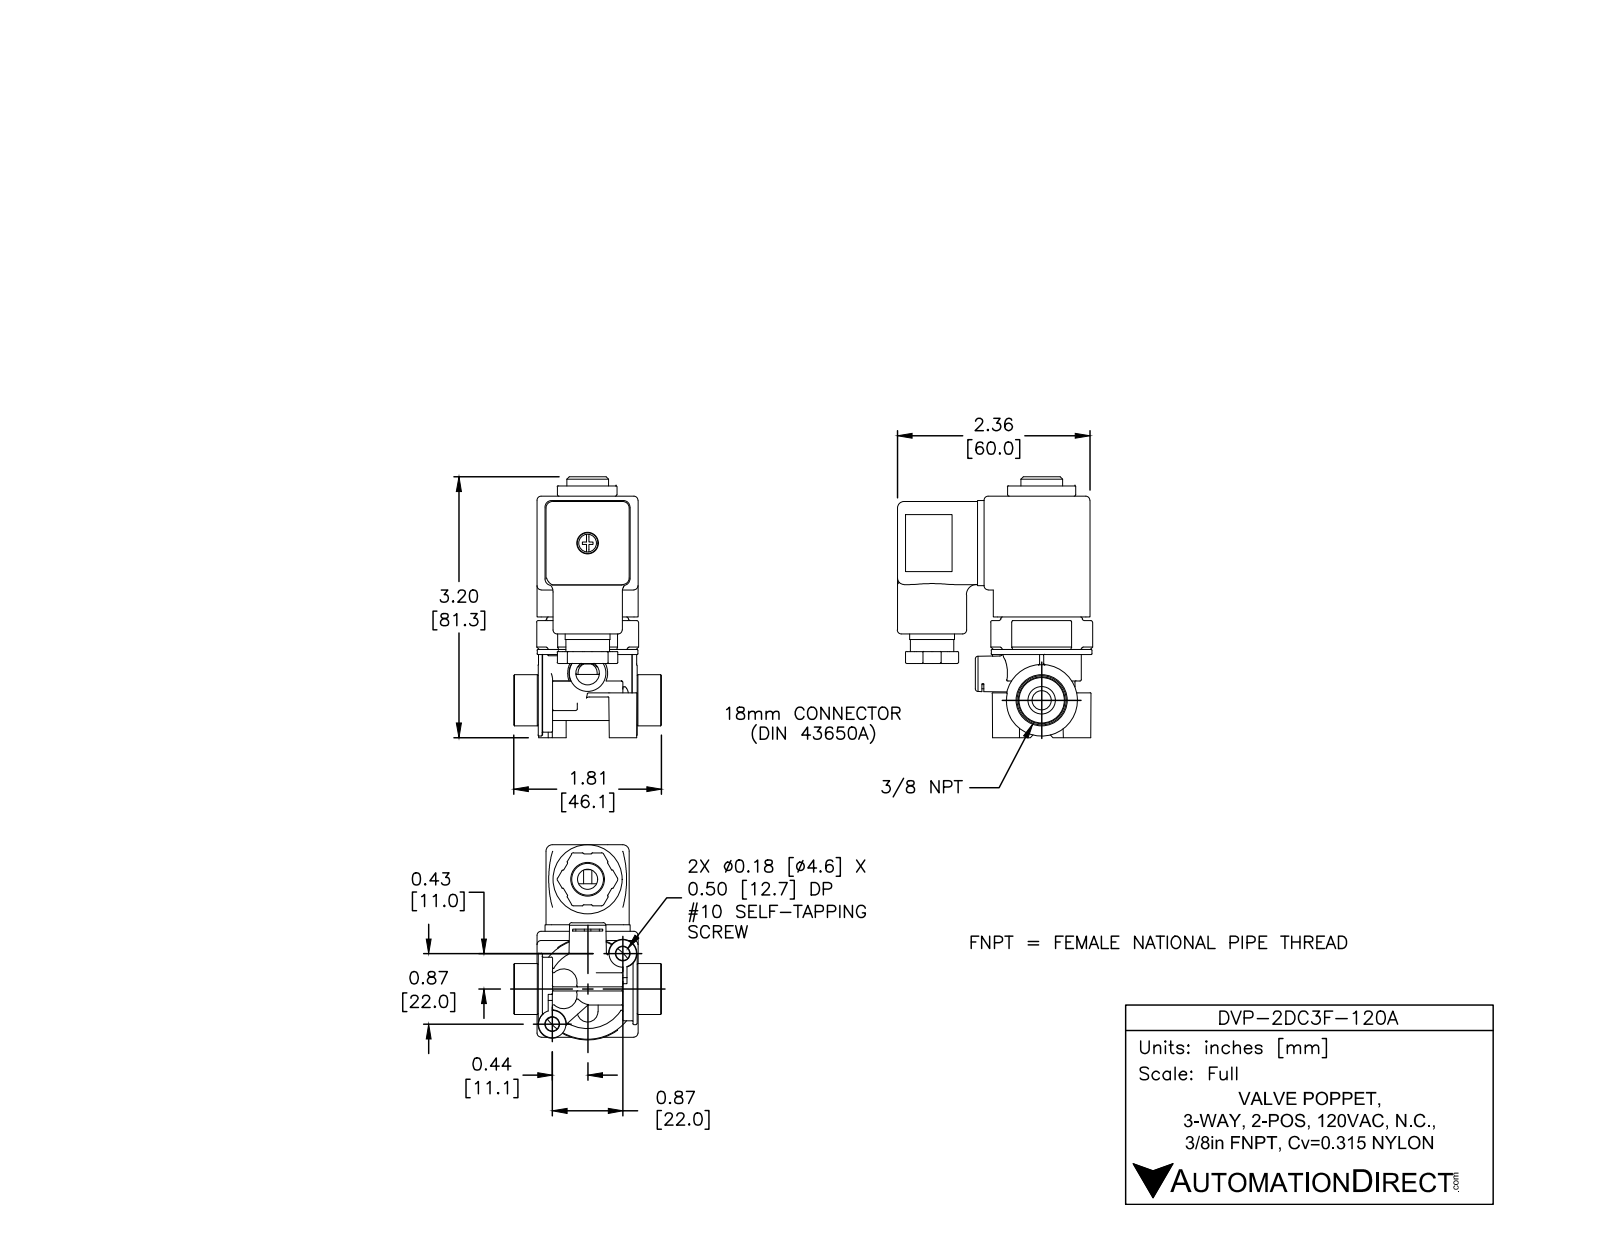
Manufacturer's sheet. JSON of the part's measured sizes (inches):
{"part_name": "DVP-2DC3F-120A", "step_written_by": "SolidWorks 2015 (AUTOMOTIVE_DESIGN)", "units": "inches", "bodies": {"solids": 2, "faces": 1760, "planar": 802, "cylindrical": 336, "other": 622}, "overall_size": [3.216, 2.395, 1.813], "volume_in3": 3.958, "surface_area_in2": 54.46, "round_holes": [[0.06, 2], [0.236, 2], [0.095, 1], [0.102, 1], [0.12, 1], [0.203, 1], [0.245, 1], [0.25, 1], [0.263, 1], [0.287, 1], [0.37, 1], [0.39, 1]], "round_bosses_or_shafts": [[0.875, 2], [0.29, 2], [1.236, 1], [1, 1], [0.972, 1], [0.875, 1], [0.85, 1], [0.78, 1]], "partial_cylinders_radius": [[0.01, 74], [0.015, 34], [0.05, 21], [0.02, 12], [0.08, 12], [0.026, 6], [0.03, 6], [0.04, 4]], "face_to_face_distances": [1.083, 1.24, 0.048, 0.157, 0.08, 0.925, 1.48, 0.109, 1.131, 0.974], "hole_center_spacings": [0.281, 0.283, 1.062, 1.343, 1.345, 1.612, 1.626, 2.184]}
